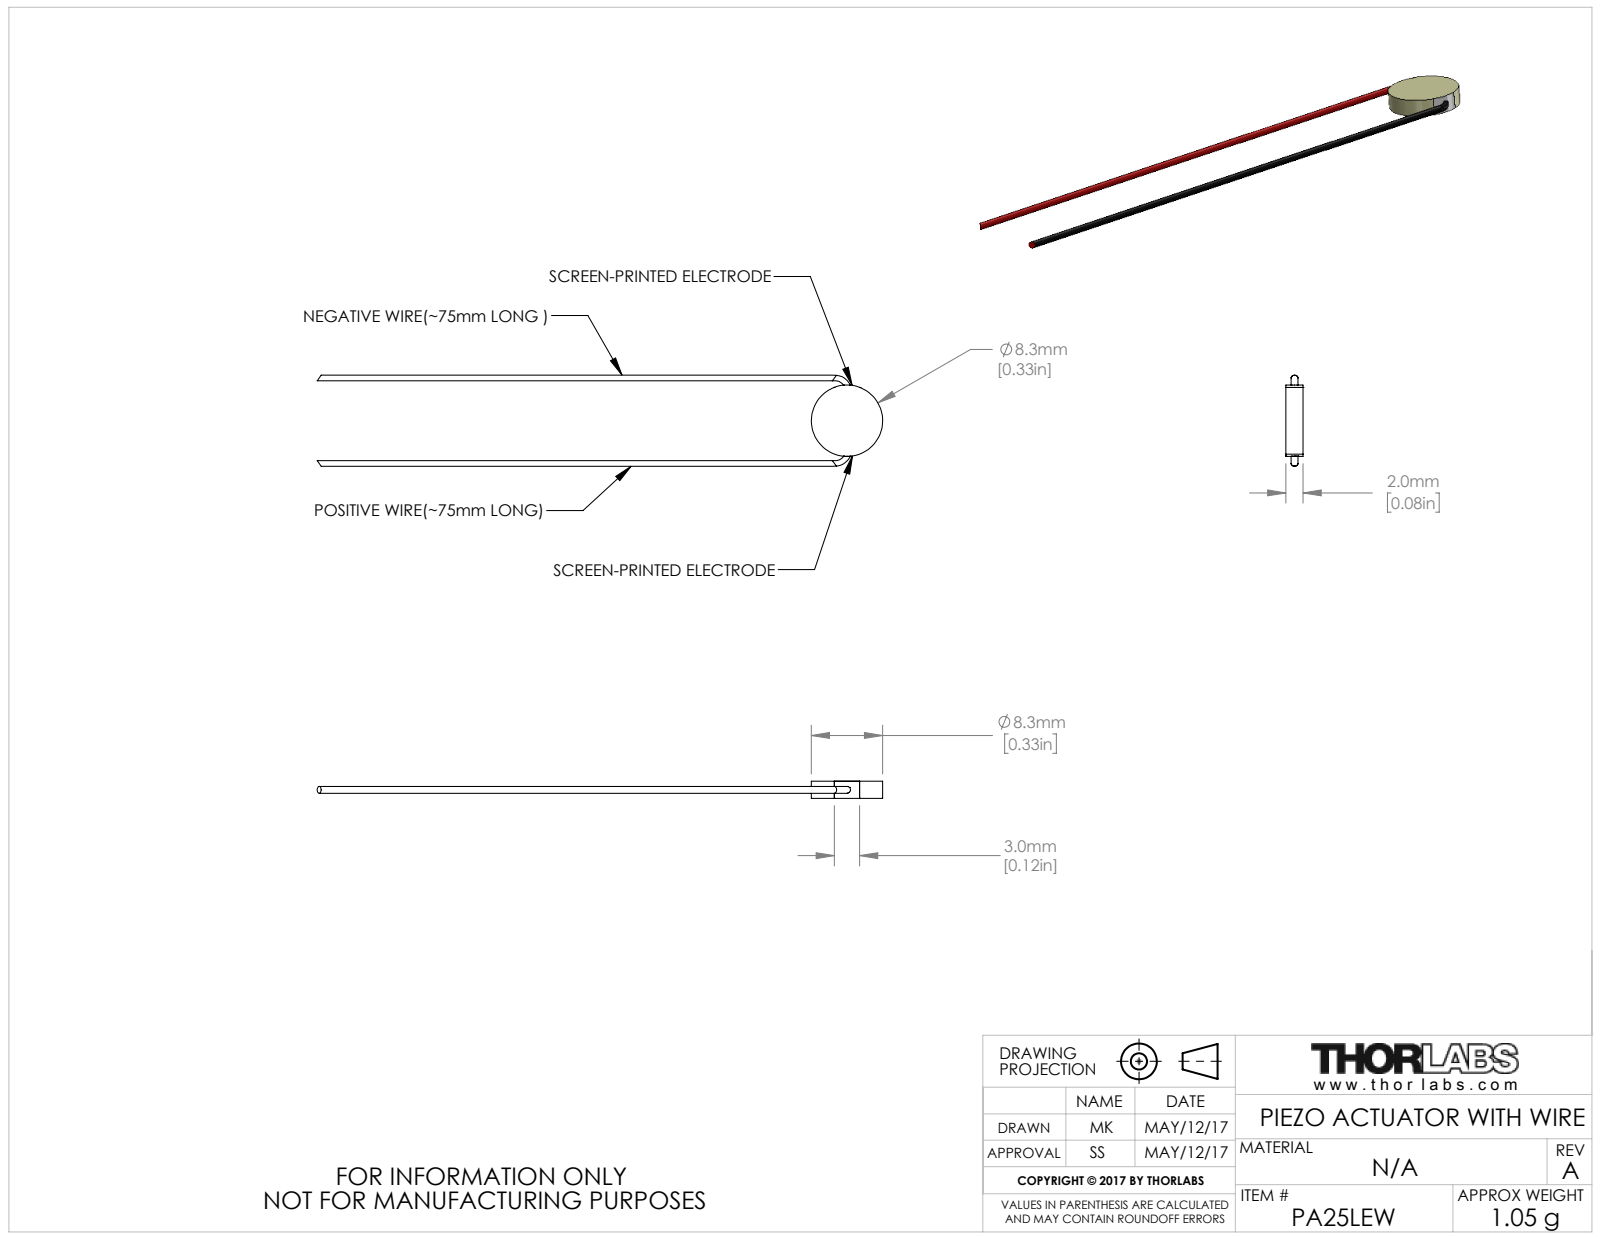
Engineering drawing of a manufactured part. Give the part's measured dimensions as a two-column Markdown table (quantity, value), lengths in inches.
| quantity | value |
| --- | --- |
| part name | CTN009555 |
| STEP written by | SolidWorks 2016 (AUTOMOTIVE_DESIGN) |
| units | inches |
| bodies | 1 solid, 36 faces (13 planar, 7 cylindrical, 16 other) |
| overall size | 2.592 × 0.418 × 0.079 |
| volume | 0.01 in³ |
| surface area | 0.688 in² |
| round bosses / shafts (diameter × count) | 0.327 × 1 |
| partial cylindrical surfaces (radius × count) | 0.163 × 1, 0.164 × 1 |
| main face-to-face distances | 0.079, 0.327, 0.078 |
